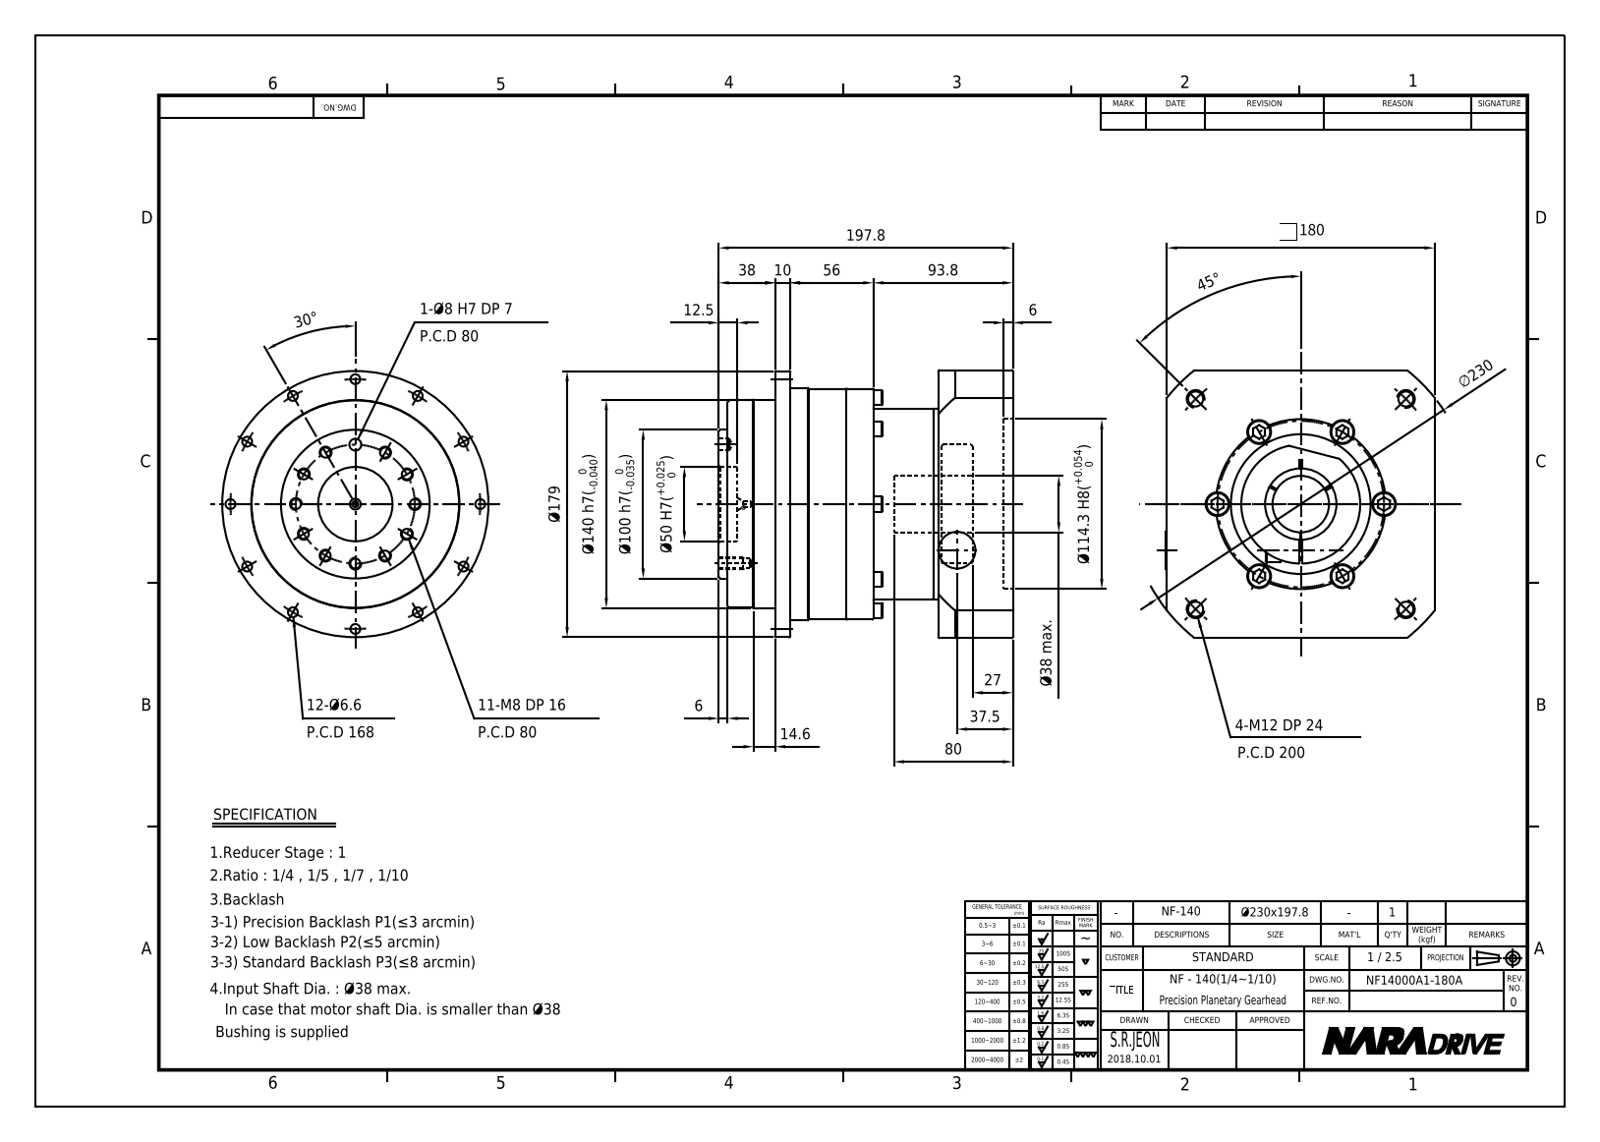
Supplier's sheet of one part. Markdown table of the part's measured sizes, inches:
| quantity | value |
| --- | --- |
| part name | NF14000A1-180A |
| STEP written by | Autodesk Inventor 2015 (AUTOMOTIVE_DESIGN) |
| units | inches |
| bodies | 1 solid, 497 faces (212 planar, 143 cylindrical, 142 other) |
| overall size | 7.787 × 7.126 × 7.087 |
| volume | 181.9 in³ |
| surface area | 517.7 in² |
| round holes (diameter × count) | 0.26 × 20, 0.262 × 17, 0.194 × 8, 0.354 × 6, 0.551 × 6, 0.398 × 4, 0.157 × 1, 0.315 × 1, 0.33 × 1, 0.433 × 1, 0.492 × 1, 0.571 × 1 |
| round bosses / shafts (diameter × count) | 0.394 × 9, 0.236 × 8, 0.512 × 6, 0.315 × 6, 6.102 × 2, 5.039 × 2, 7.047 × 1, 6.142 × 1 |
| partial cylindrical surfaces (radius × count) | 0.039 × 4, 0.354 × 1, 2.25 × 1, 4.528 × 1 |
| main face-to-face distances | 1.969, 1.89, 4.402, 0.197, 7.087, 1.693, 0.748, 2.433, 5.898, 1.496 |
| hole center spacings | 3.307, 2.917, 4.805, 5.728, 1.575, 1.712, 1.133, 2.205 |
